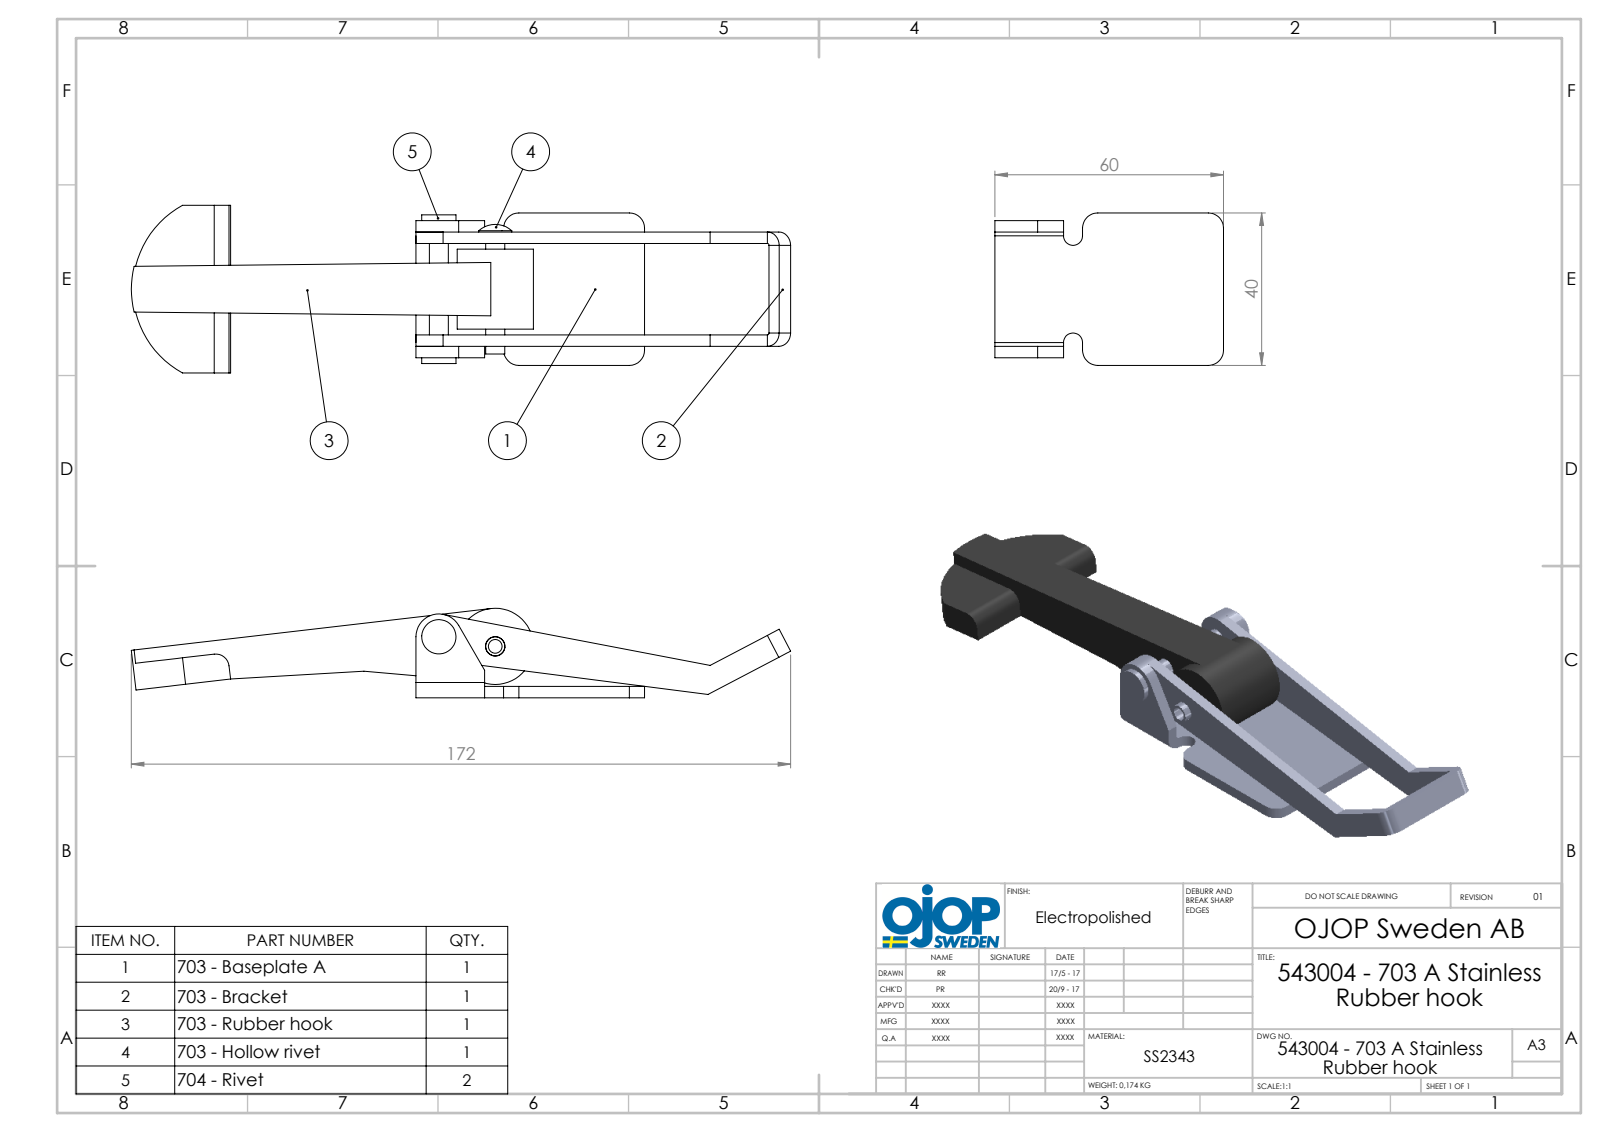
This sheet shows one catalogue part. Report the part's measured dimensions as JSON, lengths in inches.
{"part_name": "gummihake 703; nit703; 704 - Rivet Gradin; 543004 - 703 A Stainless Rubber hook (+2 more)", "step_written_by": "SolidWorks 2015 (AUTOMOTIVE_DESIGN)", "units": "inches", "bodies": {"solids": 6, "faces": 128, "planar": 67, "cylindrical": 55, "other": 6}, "overall_size": [6.814, 1.732, 0.929], "volume_in3": 2.397, "surface_area_in2": 33.04, "round_holes": [[0.201, 2], [0.098, 1], [0.217, 1], [0.283, 1]], "round_bosses_or_shafts": [[0.197, 2], [0.787, 1], [0.354, 1], [0.276, 1]], "partial_cylinders_radius": [[0.157, 6], [0.138, 3], [0.02, 2], [0.039, 2], [0.098, 2], [0.236, 1], [0.984, 1]], "face_to_face_distances": [0.118, 1.063, 1.181, 0.413, 0.945, 0.059, 0.177, 0.295, 1.004, 0.886], "hole_center_spacings": [0.591]}
